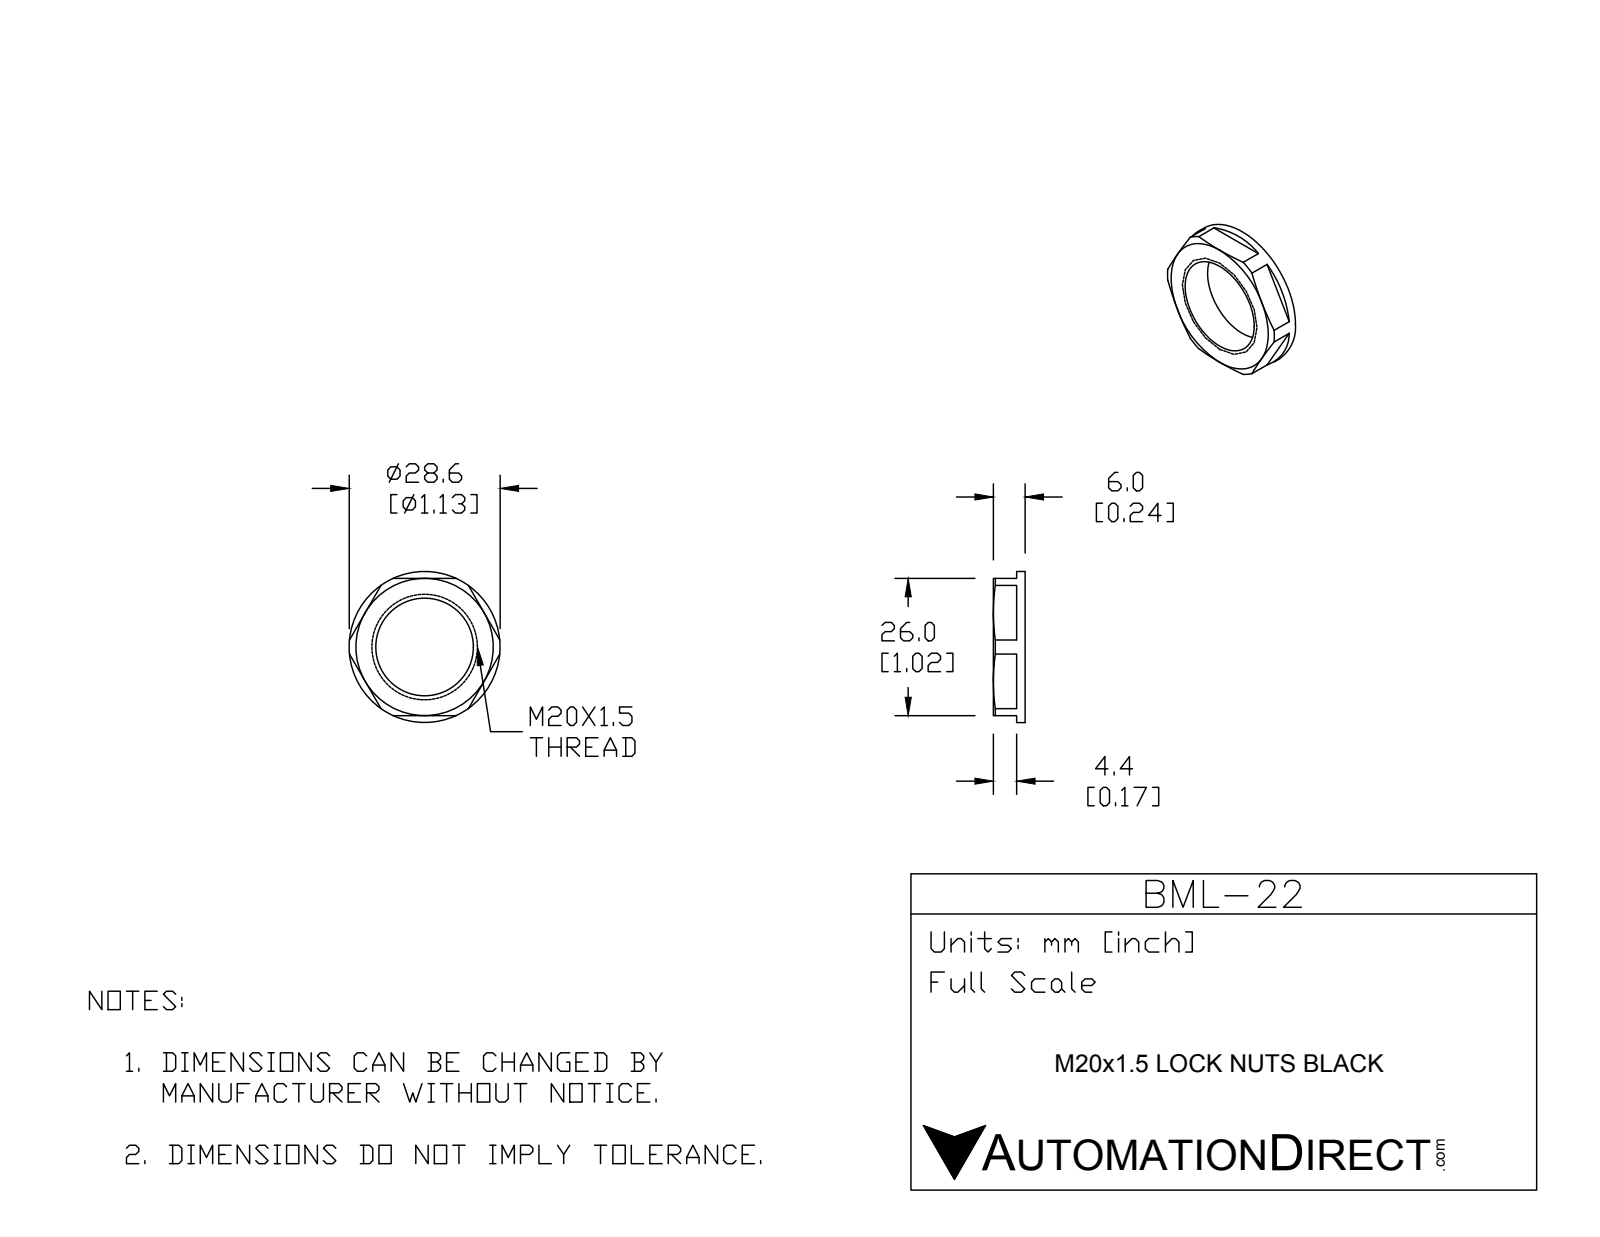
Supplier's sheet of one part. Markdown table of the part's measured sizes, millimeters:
| quantity | value |
| --- | --- |
| part name | BML-22 |
| STEP written by | SolidWorks 2015 (CONFIG_CONTROL_DESIGN) |
| units | millimeters |
| bodies | 1 solid, 33 faces (17 planar, 10 cylindrical, 6 other) |
| overall size | 28.6 × 28.6 × 6 |
| volume | 1 958 mm³ |
| surface area | 1 617 mm² |
| round holes (diameter × count) | 1.5 × 3, 18.5 × 1 |
| round bosses / shafts (diameter × count) | 28.6 × 1 |
| main face-to-face distances | 6, 26, 1.6, 4.4, 1.3, 5.7 |
| hole center spacings | 12.85, 22.26, 22.25 |
